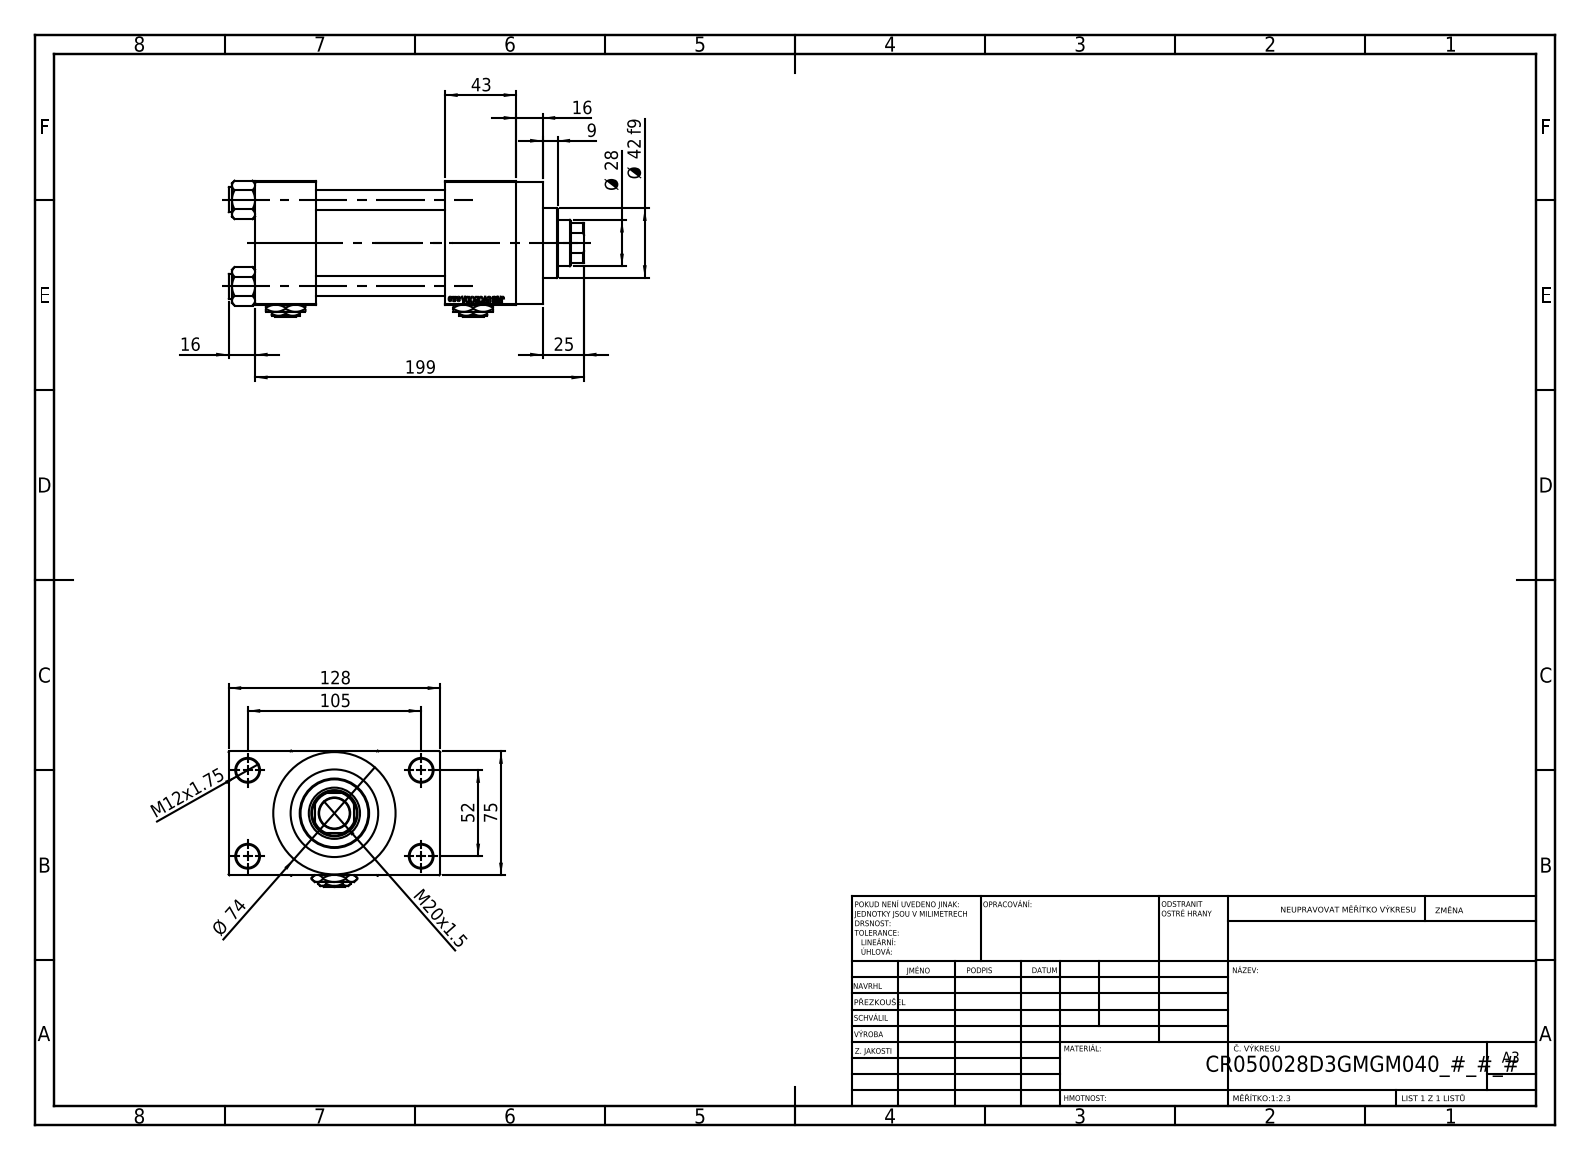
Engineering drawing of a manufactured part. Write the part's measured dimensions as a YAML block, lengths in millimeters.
part_name: "Zatka_pro_OIL_PORT; V215CR_D_Body; V215CR_D_TYCINKA; V215_VC_A (+2 more)"
step_written_by: "SolidWorks 2019 (CONFIG_CONTROL_DESIGN)"
units: millimeters
bodies: {solids: 13, faces: 1204, planar: 545, cylindrical: 99, other: 560}
overall_size: [215, 128, 82.27]
volume: 833579
surface_area: 186163
round_holes:
  - {diameter: 12, count: 4}
  - {diameter: 14, count: 4}
  - {diameter: 20.96, count: 4}
  - {diameter: 30, count: 4}
  - {diameter: 7, count: 3}
  - {diameter: 18.5, count: 1}
  - {diameter: 28, count: 1}
  - {diameter: 31, count: 1}
  - {diameter: 41, count: 1}
  - {diameter: 50, count: 1}
  - {diameter: 53, count: 1}
round_bosses_or_shafts:
  - {diameter: 15, count: 4}
  - {diameter: 74, count: 1}
  - {diameter: 56, count: 1}
  - {diameter: 42, count: 1}
partial_cylinders:
  - {radius: 13.5, count: 1}
face_to_face_distances: [75, 78, 37, 115, 26.5, 158, 121, 43, 101.5, 16]
hole_center_spacings: [26.35, 36.98, 52.3, 58.43, 58.59, 78.65, 94.37, 52]
